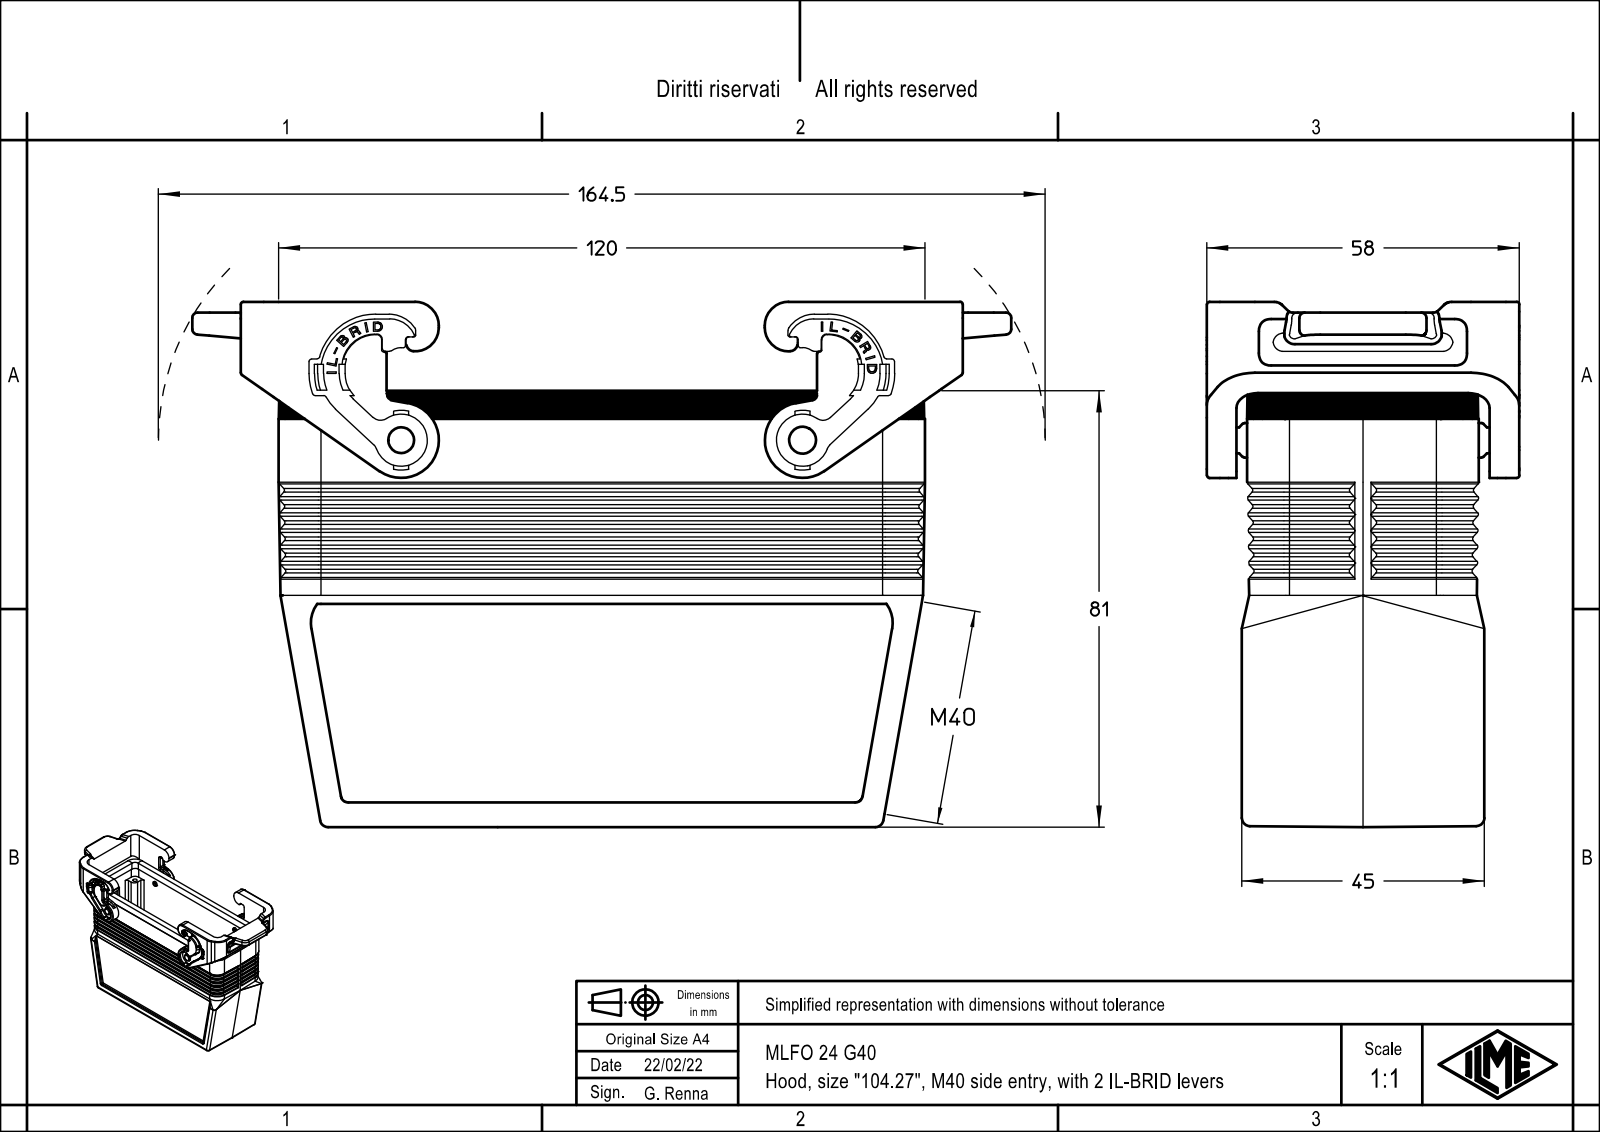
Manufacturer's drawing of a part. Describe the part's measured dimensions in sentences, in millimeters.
The part is named "MLFO_24_G40". Its 3-D file was written by "Creo Elements/Direct Modeling 20.1B 02-Apr-2019 (C) Parametric Technology GmbH (AUTOMOTIVE_DESIGN)". It is 1 solid with 1602 faces: 1031 planar, 391 cylindrical and 180 other. Overall it measures 152 by 97.45 by 58 millimeters. Its volume is 133 423 cubic millimeters and its surface area 71 417 square millimeters. Round holes: 4 of diameter 2.75, 1 of diameter 38.6. Round bosses or shafts: 2 of diameter 6.8, 2 of diameter 4.8. Partial cylindrical surfaces (rounded edges, fillets, slot ends): 104 of radius 0.5, 46 of radius 1, 20 of radius 3, 16 of radius 7, 15 of radius 0.33, 14 of radius 1.5, 8 of radius 0.3, 8 of radius 2. The main face-to-face distances are 39.25, 3.75, 2, 1, 43, 4.75, 5.75, 35.5, 34.5, 38.25. The hole center spacings are 27, 104, 107.45.
